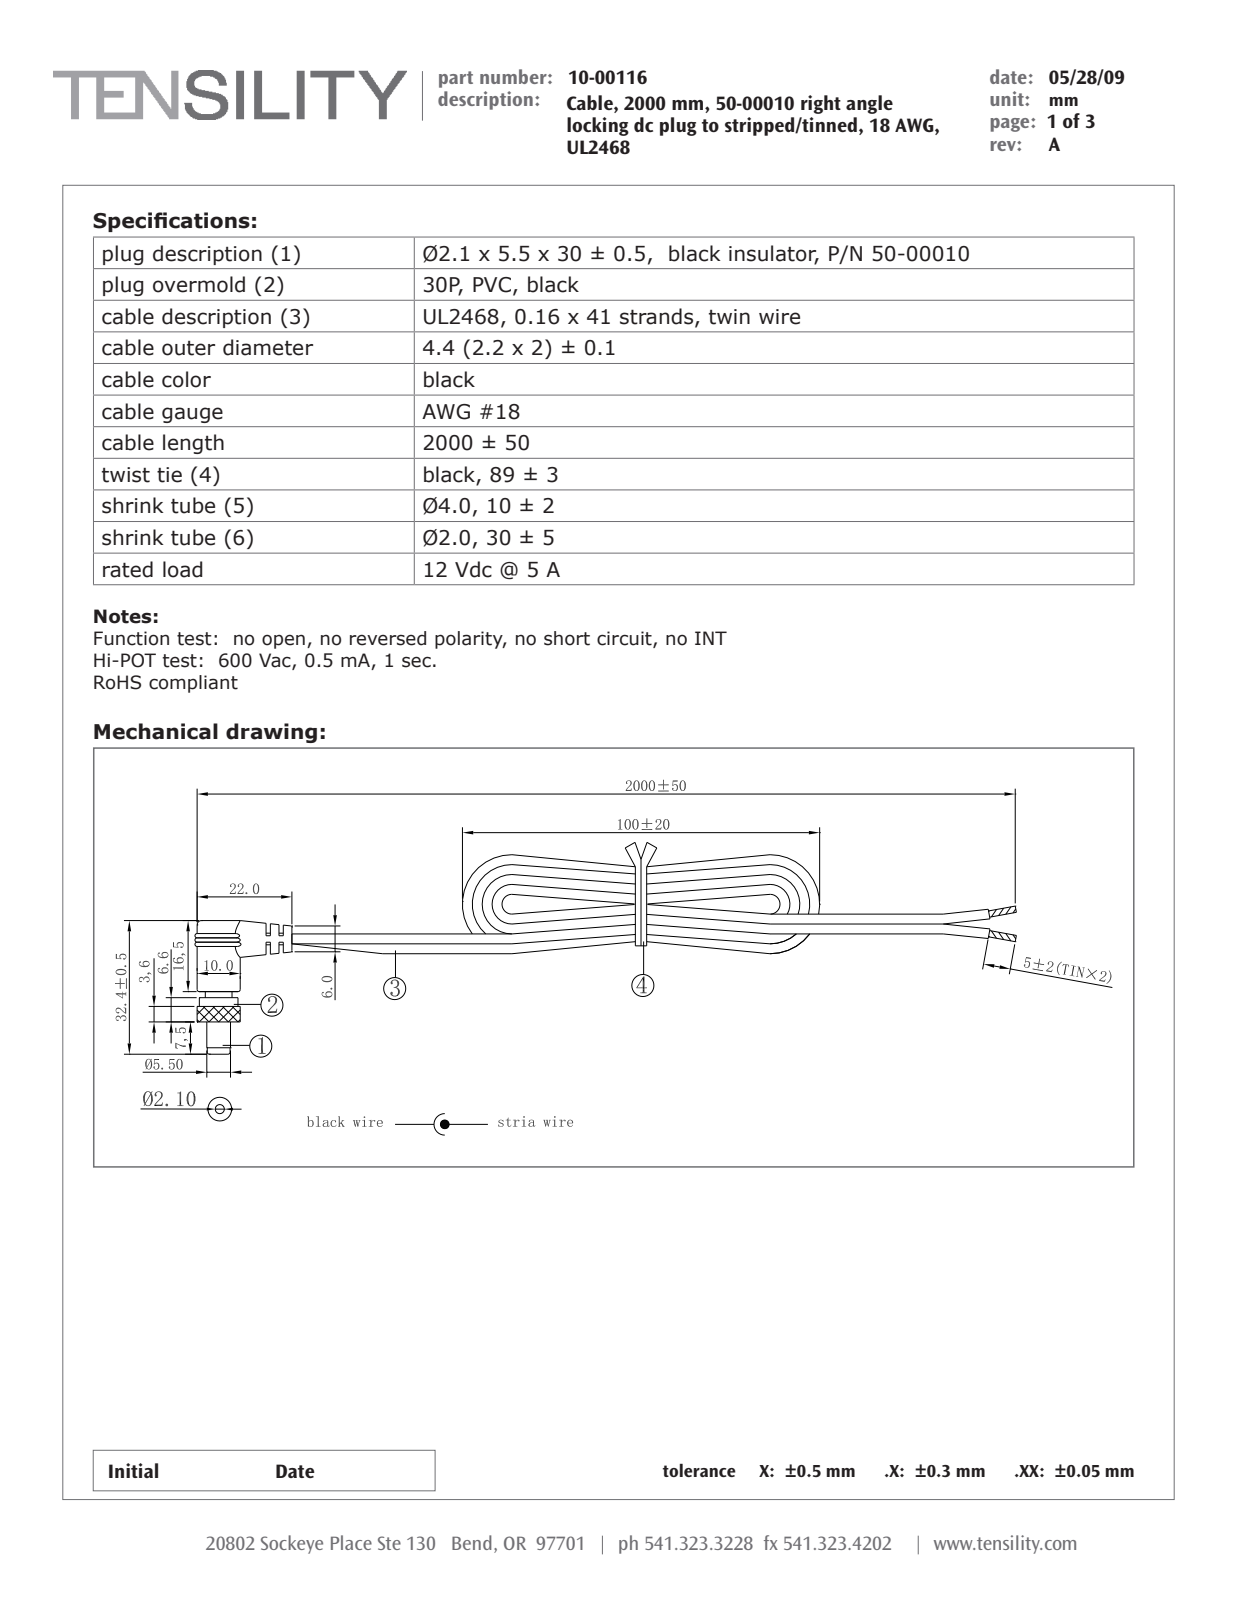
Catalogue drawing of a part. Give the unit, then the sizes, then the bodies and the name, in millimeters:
Units: millimetres
Overall size (bounding box): 176.5 × 32.4 × 11
Round holes (diameter × count): ⌀1.6 ×1, ⌀2.1 ×1, ⌀2.16 ×1, ⌀2.6 ×1, ⌀2.85 ×1, ⌀3.85 ×1, ⌀5.04 ×1, ⌀5.44 ×1, ⌀5.5 ×1, ⌀5.65 ×1, ⌀6.4 ×1, ⌀7.25 ×1
Round bosses / shafts (diameter × count): ⌀10 ×2, ⌀2.2 ×2, ⌀11 ×1, ⌀8.5 ×1, ⌀7 ×1, ⌀6.2 ×1, ⌀6 ×1, ⌀5.48 ×1
Partial cylindrical surfaces — rounded edges, fillets, slot ends (radius × count): R0.75 ×2, R0.16 ×1
Main face-to-face distances: 1, 2, 3, 5.03, 16.5, 11.47, 24.9, 19.87, 8.4, 4
Hole centre spacings: 0.32, 0.33, 0.47, 0.5, 0.59, 0.49, 0.43, 0.46
Volume: 3 722 mm³ · Surface area: 19 124 mm²
Bodies: 179 solids, 2762 faces (1098 planar, 798 cylindrical, 866 other)
Part name (STEP PRODUCT): 50-00010 interior shell; 24-00017; 50-00010 pin; 30-00007_Stripped and tinned 5mm (+6 more)
STEP written by: SolidWorks 2015 (CONFIG_CONTROL_DESIGN)
